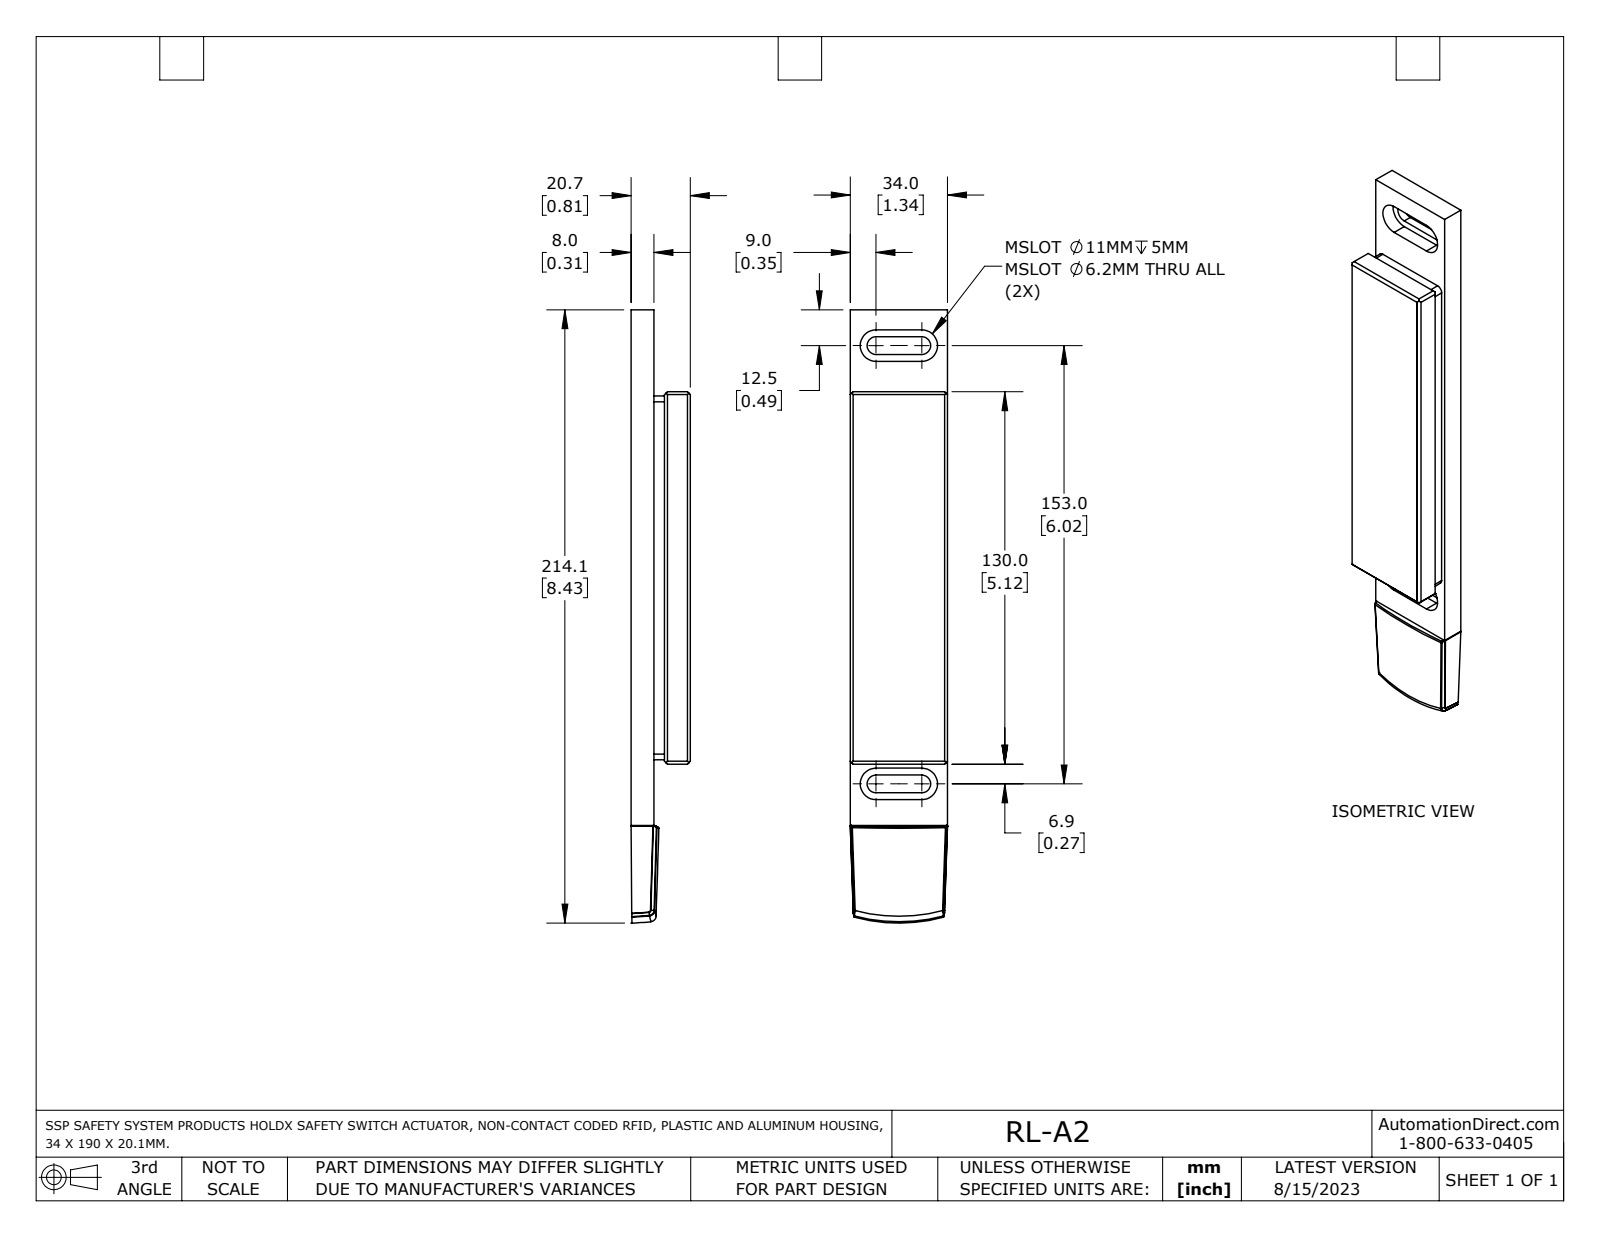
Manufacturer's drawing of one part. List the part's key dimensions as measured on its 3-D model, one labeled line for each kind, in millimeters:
Part name (STEP PRODUCT): RL-A1_REV1
STEP written by: SolidWorks 2021 (AUTOMOTIVE_DESIGN)
Units: millimetres
Bodies: 1 solid, 100 faces (52 planar, 17 cylindrical, 31 other)
Overall size (bounding box): 214.1 × 34 × 20.7
Volume: 108 000 mm³ · Surface area: 23 890 mm²
Round holes (diameter × count): ⌀16 ×1
Round bosses / shafts (diameter × count): ⌀11.8 ×1
Partial cylindrical surfaces — rounded edges, fillets, slot ends (radius × count): R2 ×4, R3.1 ×4, R5.5 ×4, R0.3 ×2, R75 ×1
Main face-to-face distances: 20.7, 34, 12.7, 8, 1.5, 32.5, 31, 29, 3, 17.7
